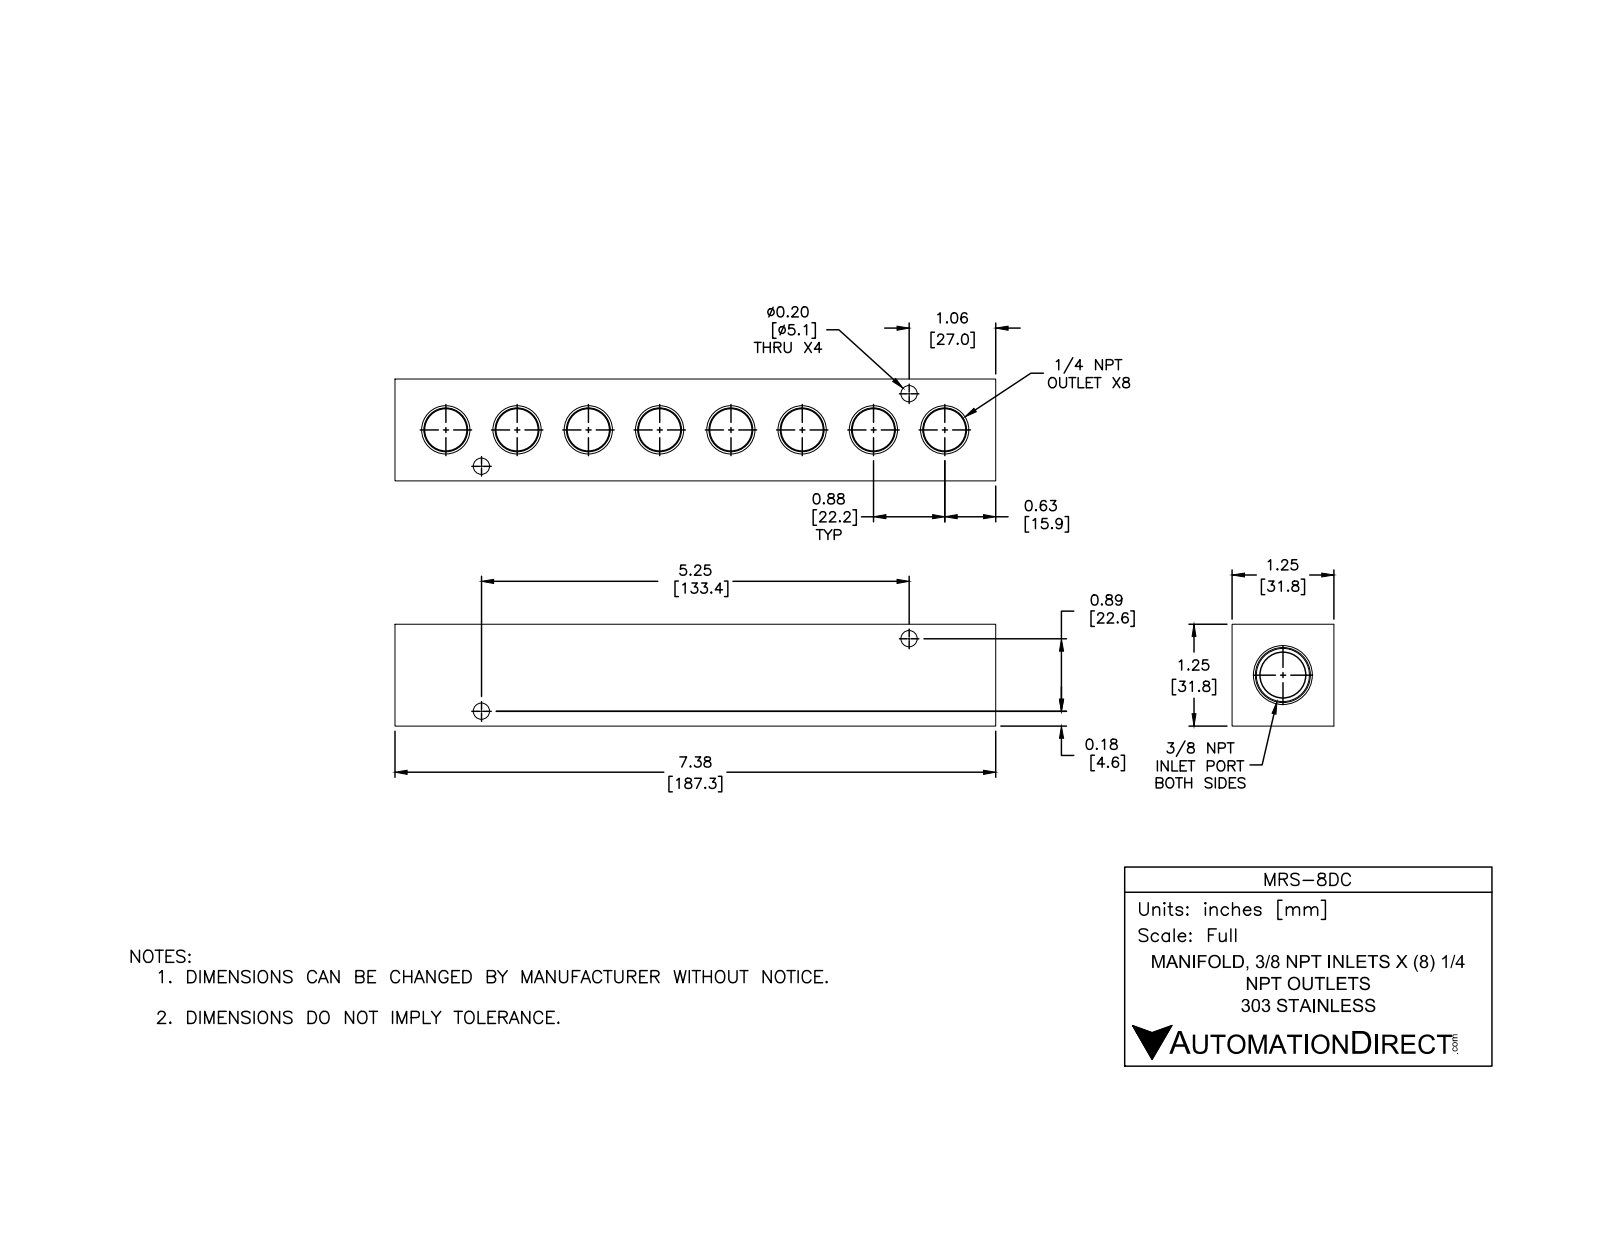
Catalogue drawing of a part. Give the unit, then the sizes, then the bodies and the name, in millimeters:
Units: millimetres
Overall size (bounding box): 187.3 × 31.8 × 31.8
Round holes (diameter × count): ⌀5.1 ×4, ⌀14.3 ×1
Partial cylindrical surfaces — rounded edges, fillets, slot ends (radius × count): R5.6 ×8
Main face-to-face distances: 31.8, 187.3, 21.8, 9.9, 10.4, 176.9, 166.5
Hole centre spacings: 135.2
Volume: 144 300 mm³ · Surface area: 36 850 mm²
Bodies: 1 solid, 98 faces (24 planar, 34 cylindrical, 40 other)
Part name (STEP PRODUCT): MRS-8DC
STEP written by: SolidWorks 2015 (CONFIG_CONTROL_DESIGN)
